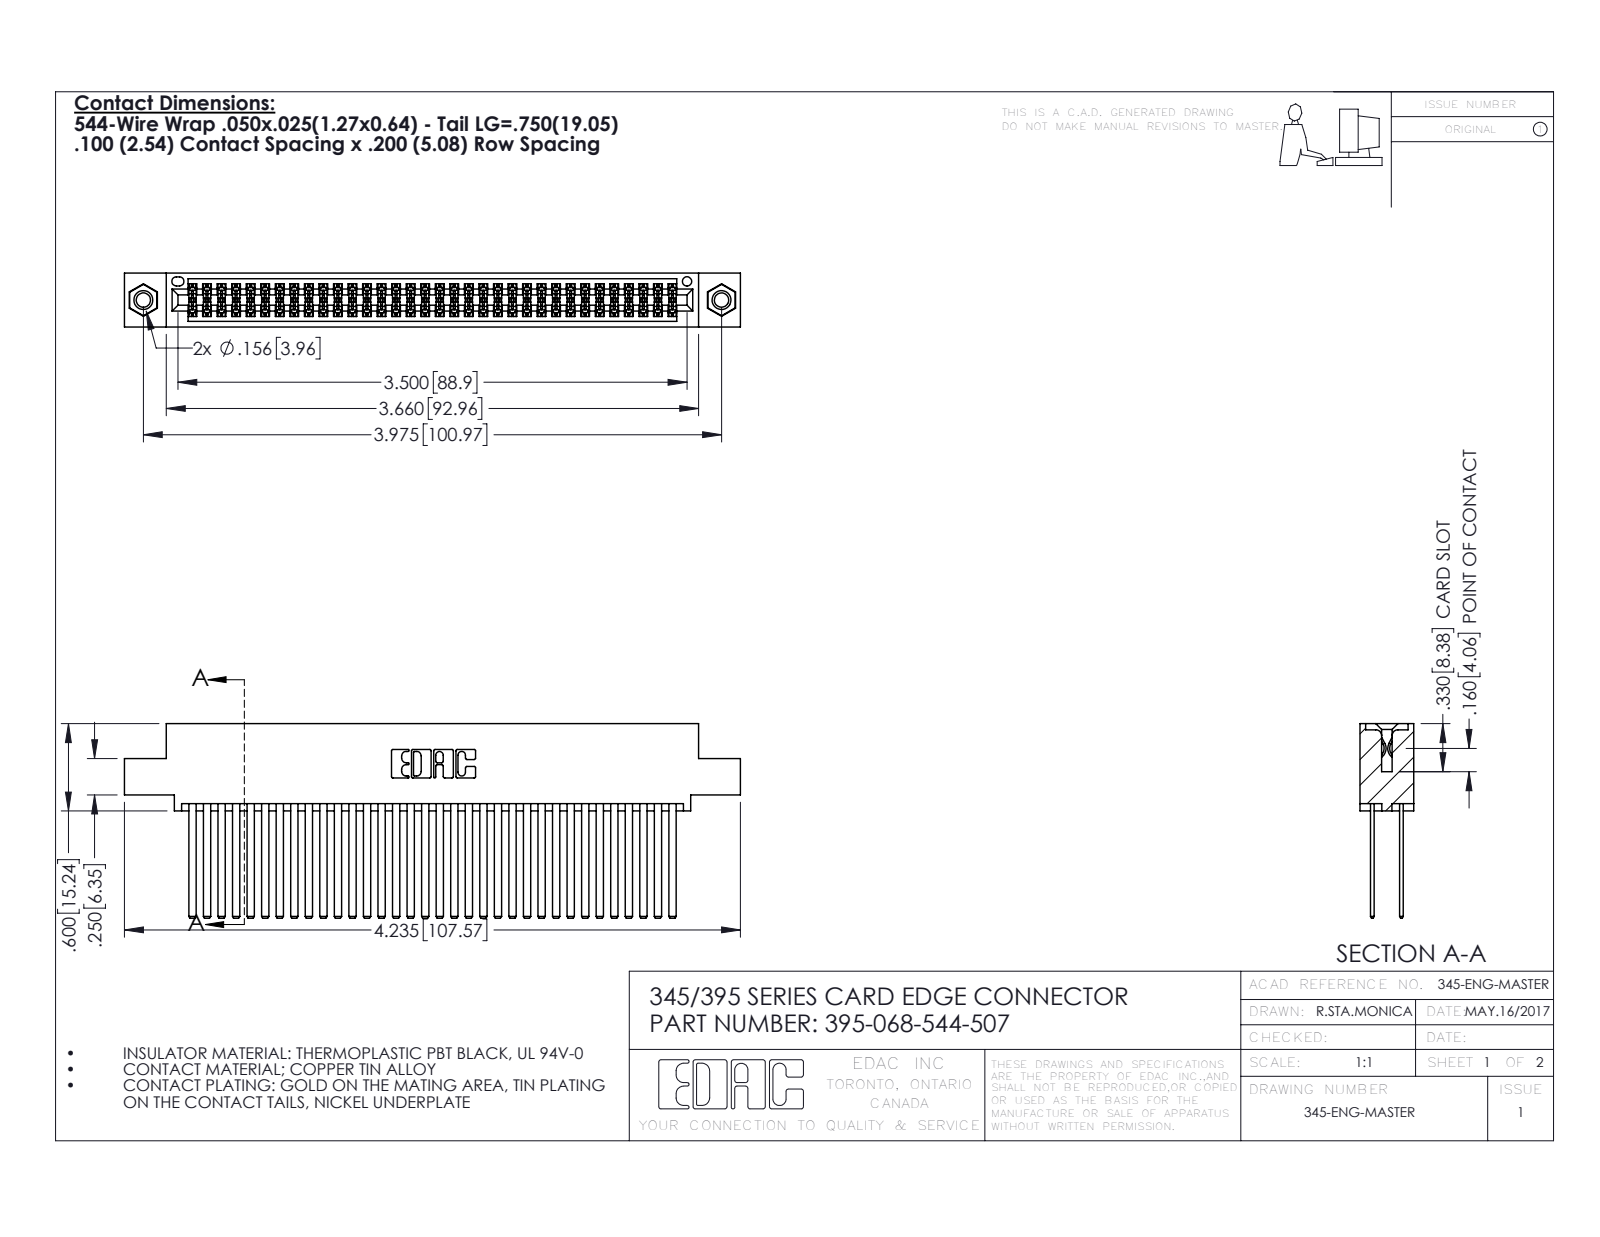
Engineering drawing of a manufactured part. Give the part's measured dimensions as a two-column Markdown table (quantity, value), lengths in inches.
| quantity | value |
| --- | --- |
| part name | 395-068-544-507; 345-250-001_345-250-005-103; 345-292-001_345-293-144; 345 Part_0.110 Offset - 0.156 Dia-TI |
| STEP written by | SolidWorks 2016 (CONFIG_CONTROL_DESIGN) |
| units | inches |
| bodies | 71 solids, 3182 faces (2088 planar, 1078 cylindrical, 16 other) |
| overall size | 4.235 × 1.337 × 0.37 |
| volume | 0.686 in³ |
| surface area | 30.03 in² |
| round holes (diameter × count) | 0.098 × 2, 0.125 × 2, 0.156 × 2, 0.064 × 1 |
| round bosses / shafts (diameter × count) | 0.155 × 2 |
| partial cylindrical surfaces (radius × count) | 0.006 × 102, 0.01 × 22, 0.007 × 6, 0.031 × 6, 0.026 × 3, 0.014 × 2, 0.019 × 2, 0.022 × 2 |
| main face-to-face distances | 0.2, 0.025, 0.072, 0.098, 0.272, 0.298, 0.225, 0.175, 0.37, 0.05 |
| hole center spacings | 0.27, 3.74, 3.975 |
